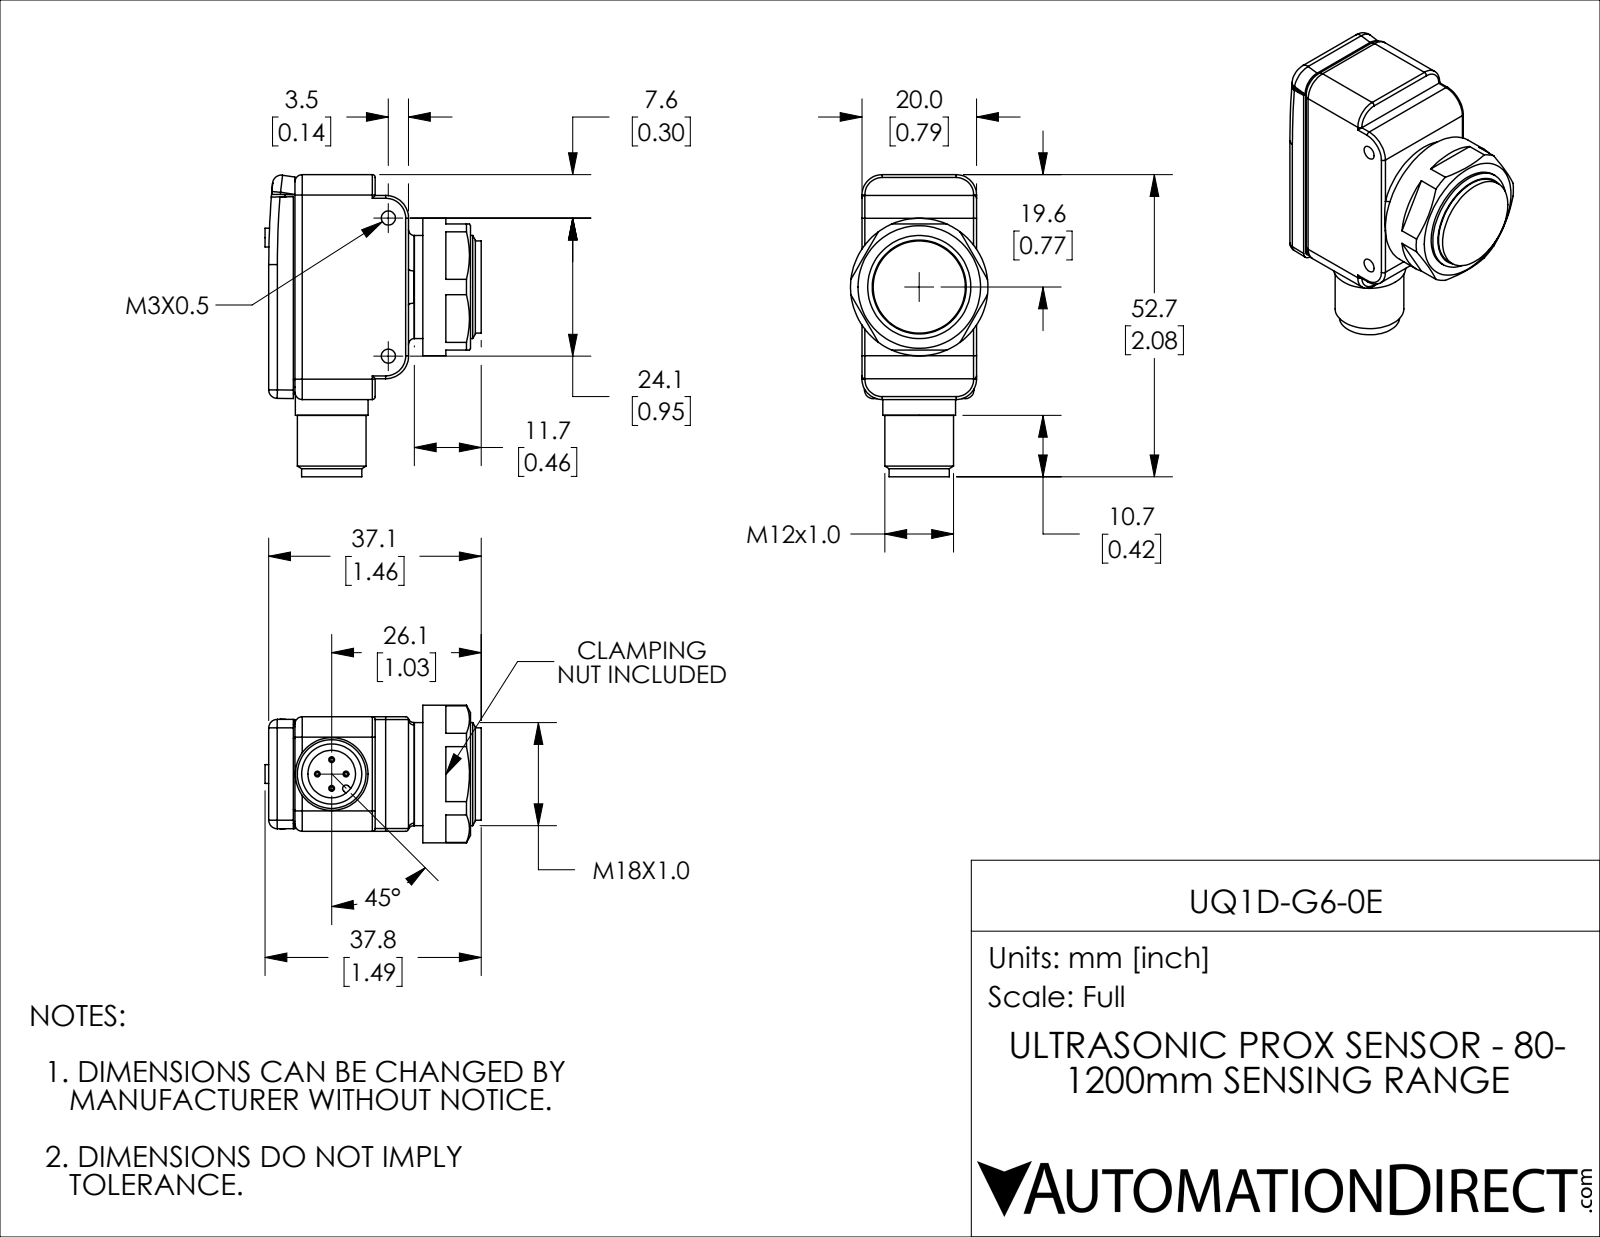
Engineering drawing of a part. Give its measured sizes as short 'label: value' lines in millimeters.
name: UQ1D-G6-0E
written by: SolidWorks 2018 (AUTOMOTIVE_DESIGN)
unit: mm
bodies: 7 solids, 203 faces (81 planar, 72 cylindrical, 50 other)
size: 52.73 × 37.75 × 24
volume: 22 757 mm³; area: 11 051 mm²
holes: 2× ⌀2.46, 1× ⌀3.3, 1× ⌀8.3
bosses: 4× ⌀1, 1× ⌀24, 1× ⌀18, 1× ⌀16.1, 1× ⌀12.7, 1× ⌀12, 1× ⌀10.5
rounds: 10× R0.5, 6× R1.5, 4× R1.25, 4× R3.55, 2× R3, 2× R4, 2× R150, 1× R0.6
face distances: 2.3, 20, 23.13, 20.83, 2.29, 4.59, 25.42, 11.67, 37.09, 34.8
hole spacings: 24.1
